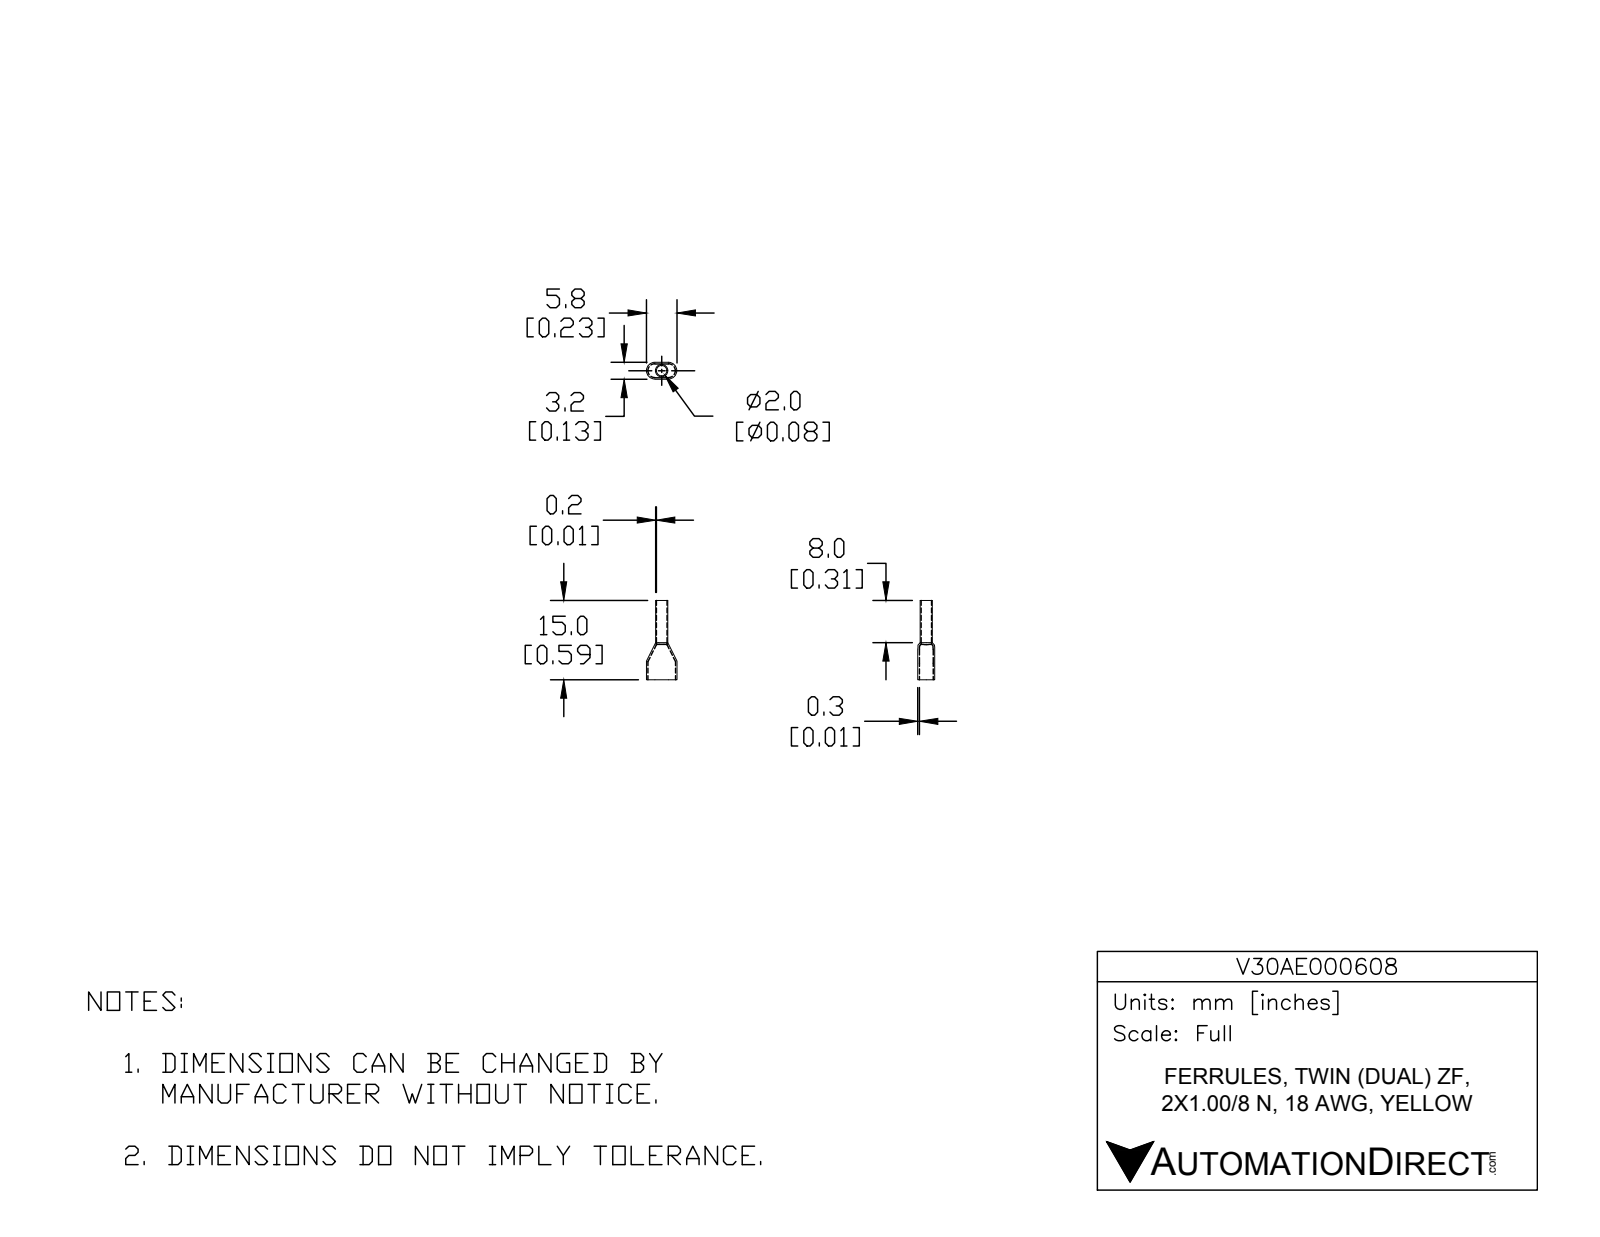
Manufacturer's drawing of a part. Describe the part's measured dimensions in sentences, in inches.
The part is named "V30AE000608". Its 3-D file was written by "SolidWorks 2017 (AUTOMOTIVE_DESIGN)". It is 2 solids with 36 faces: 14 planar, 22 cylindrical and 0 other. Overall it measures 0.591 by 0.228 by 0.126 inches. Its volume is 0.002 cubic inches and its surface area 0.456 square inches. Round holes: 1 of diameter 0.079. Round bosses or shafts: 1 of diameter 0.091. Partial cylindrical surfaces (rounded edges, fillets, slot ends): 4 of radius 0.051, 4 of radius 0.063. The main face-to-face distances are 0.114, 0.102, 0.126, 0.276, 0.591, 0.315, 0.264, 0.327.
